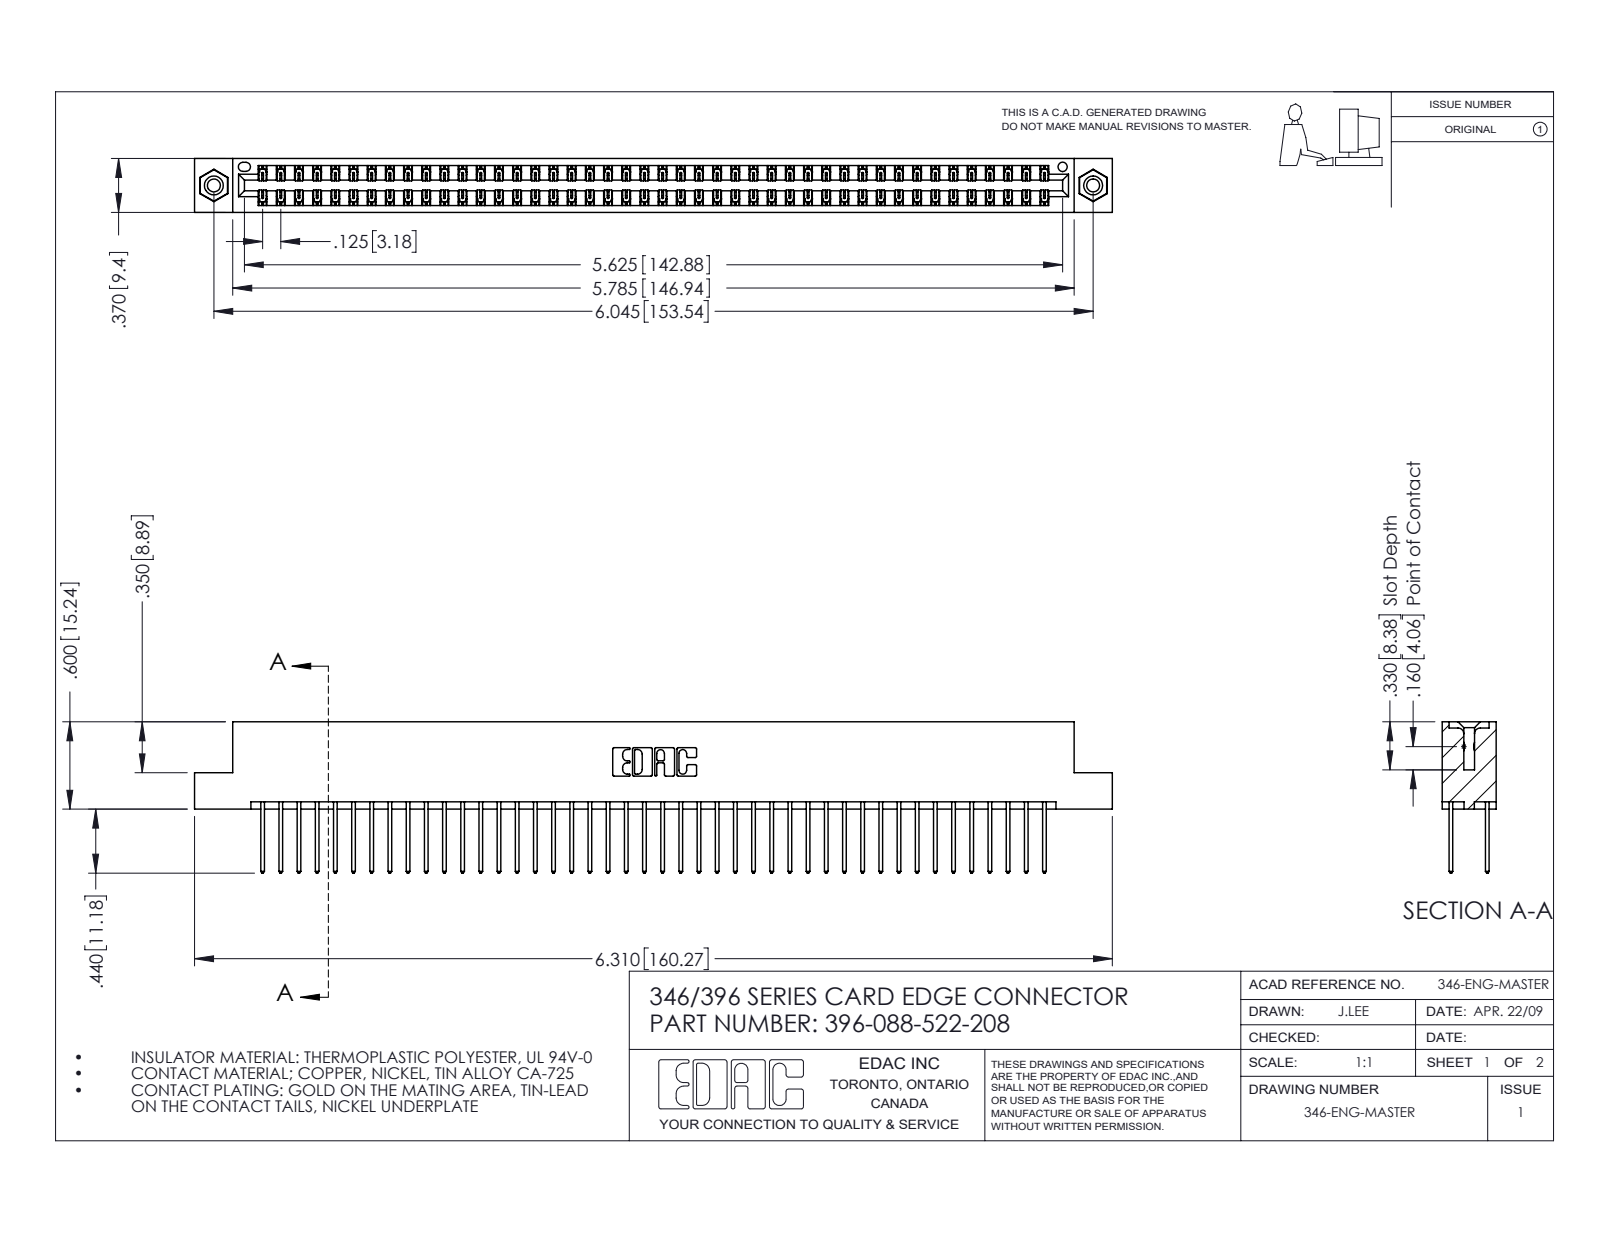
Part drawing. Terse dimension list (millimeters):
name: 346 Part_Flush Mounting Lugs - 0.156 Dia-TI; 396-088-522-208; 345-292-001_345-293-122; 345-250-001_345-250-003-102
written by: SolidWorks 2016 (CONFIG_CONTROL_DESIGN)
unit: mm
bodies: 91 solids, 4758 faces (3188 planar, 1554 cylindrical, 16 other)
size: 160.3 × 26.4 × 9.4
volume: 15 900 mm³; area: 22 900 mm²
holes: 2× ⌀2.3, 2× ⌀3.2, 2× ⌀4, 1× ⌀1.6
bosses: 2× ⌀3.9
rounds: 132× R0.2, 88× R0.3, 22× R0.3, 6× R0.2, 6× R0.8, 3× R0.7, 2× R0.4, 2× R0.6
face distances: 1.2, 8.2, 6.4, 9.4, 1.8, 7.6, 0.6, 7, 3.8, 5.6
hole spacings: 6.2, 148.2, 153.5
